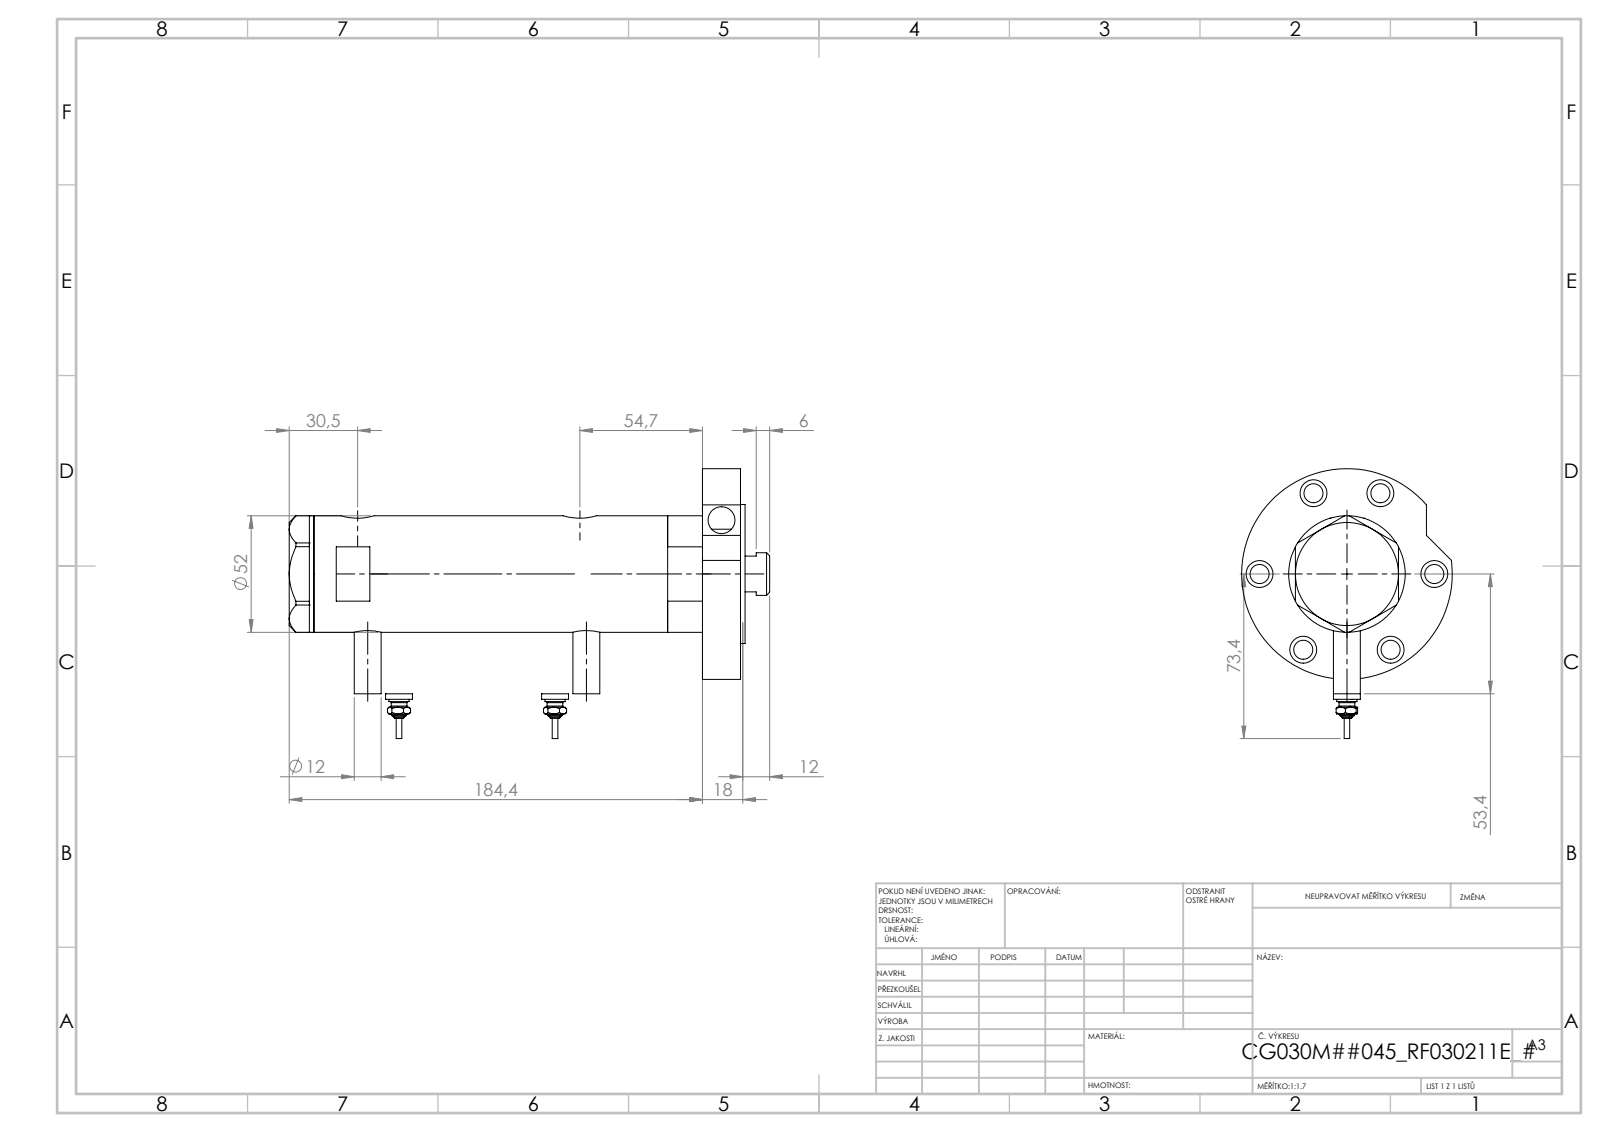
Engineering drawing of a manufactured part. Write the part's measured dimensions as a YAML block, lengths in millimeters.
part_name: "V270CG_FRONT; V270CG_VC; V270CG_BACK; V270CG_MIDDLE (+2 more)"
step_written_by: "SolidWorks 2019 (CONFIG_CONTROL_DESIGN)"
units: millimeters
bodies: {solids: 7, faces: 290, planar: 106, cylindrical: 110, other: 74}
overall_size: [194.02, 105.3, 94]
volume: 430082
surface_area: 105238
round_holes:
  - {diameter: 12, count: 7}
  - {diameter: 8.5, count: 6}
  - {diameter: 5, count: 2}
  - {diameter: 9.73, count: 2}
  - {diameter: 12.5, count: 2}
  - {diameter: 15, count: 2}
  - {diameter: 6.5, count: 1}
  - {diameter: 20, count: 1}
  - {diameter: 21.5, count: 1}
  - {diameter: 30, count: 1}
  - {diameter: 33, count: 1}
  - {diameter: 40, count: 1}
round_bosses_or_shafts:
  - {diameter: 12, count: 3}
  - {diameter: 9, count: 2}
  - {diameter: 7, count: 2}
  - {diameter: 4.34, count: 2}
  - {diameter: 2.4, count: 2}
  - {diameter: 94, count: 1}
  - {diameter: 62, count: 1}
  - {diameter: 52, count: 1}
face_to_face_distances: [17, 150.44, 167.44, 51.9, 2, 169.44, 98.54, 68.9, 70.9, 19]
hole_center_spacings: [39, 2.9, 4.5, 43.34, 64.85, 67.55, 69.95, 71.75]
